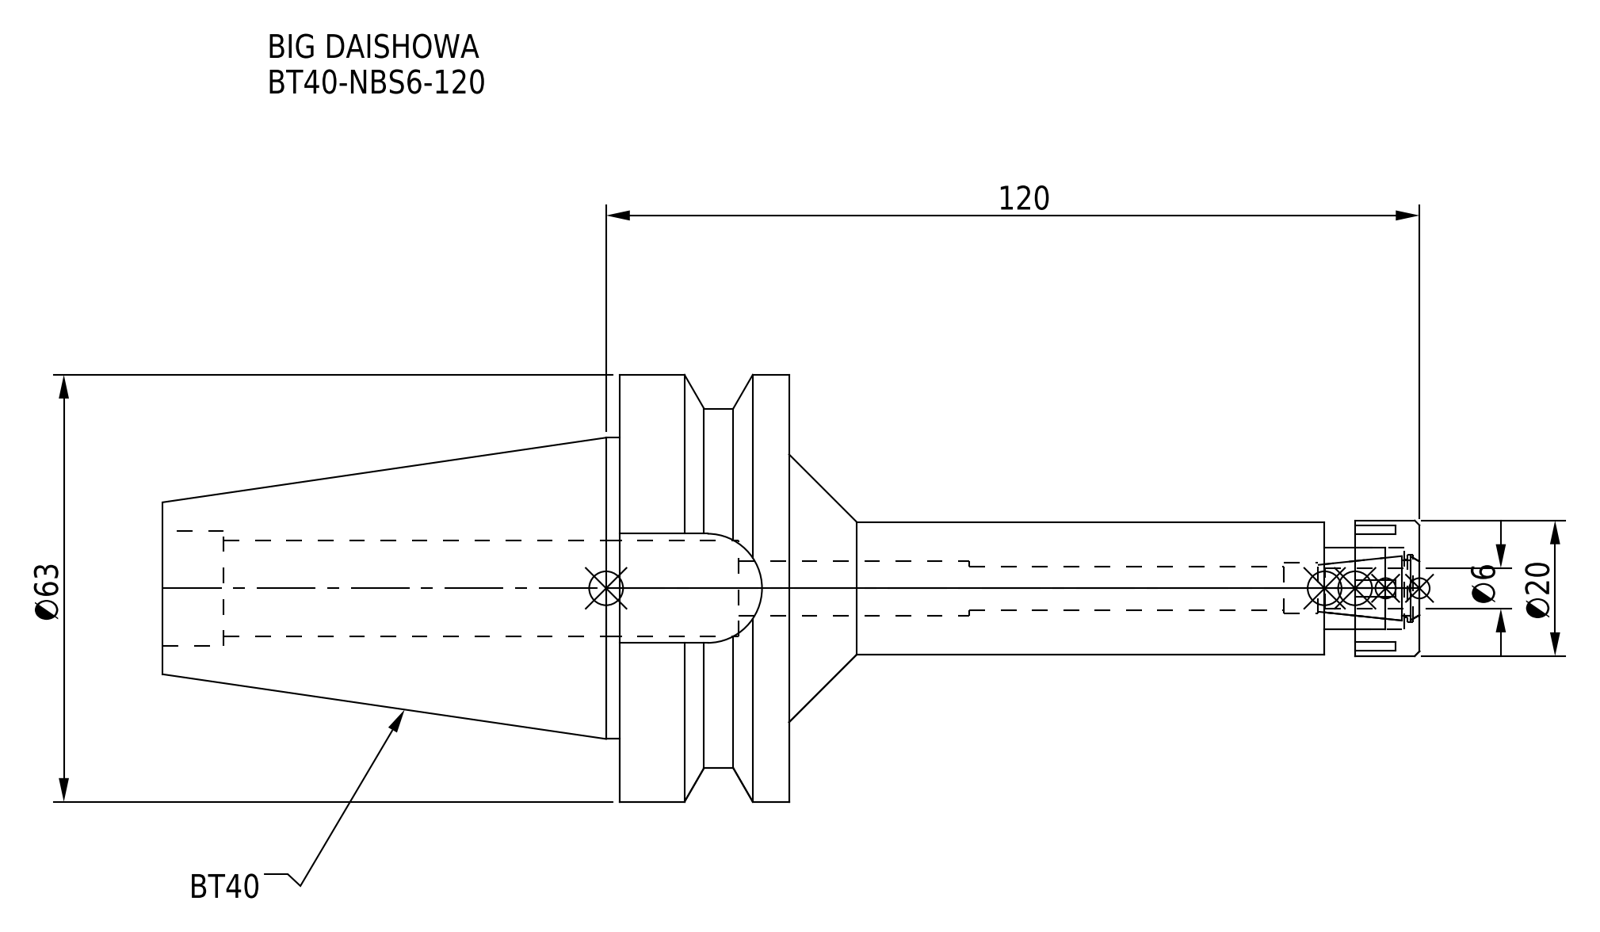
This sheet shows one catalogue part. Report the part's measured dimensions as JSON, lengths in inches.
{"part_name": "BT40-NBS6-120; BT40-NBS6-120.stp; BT40-NBS6-120_1.stp; BT40-NBS6-120-FreeParts (+3 more)", "step_written_by": "SolidWorks 2019 (CONFIG_CONTROL_DESIGN)", "units": "inches", "bodies": {"solids": 2, "faces": 93, "planar": 45, "cylindrical": 34, "other": 14}, "overall_size": [7.299, 2.48, 2.48], "volume_in3": 8.964, "surface_area_in2": 48.35, "round_holes": [[0.252, 1], [0.295, 1], [0.315, 1], [0.335, 1], [0.394, 1], [0.472, 1], [0.559, 1], [0.669, 1]], "round_bosses_or_shafts": [[2.48, 1], [2.087, 1], [1.75, 1], [0.787, 1], [0.768, 1]], "partial_cylinders_radius": [[0.317, 1]], "face_to_face_distances": [0.984, 1.772, 3.638, 2.654, 6.748, 0.177, 3.661, 4.646, 7.299, 0.551]}
